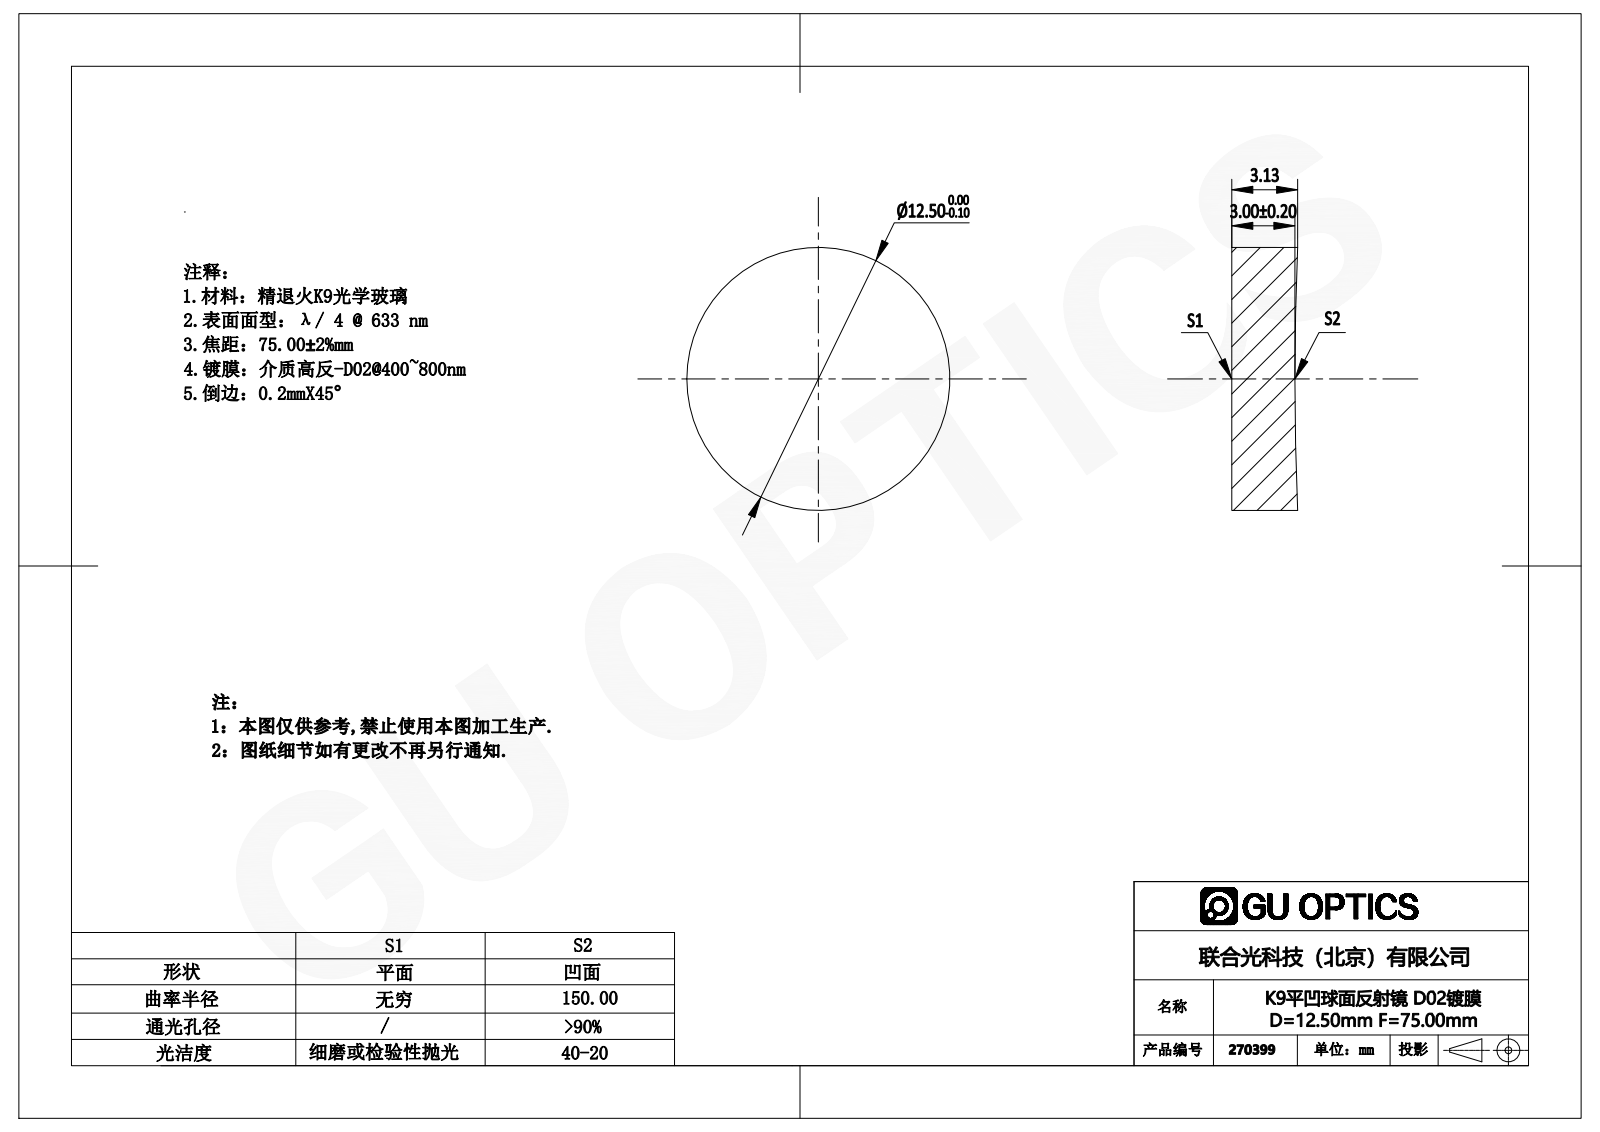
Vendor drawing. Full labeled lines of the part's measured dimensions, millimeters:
Part name (STEP PRODUCT): 270009
STEP written by: SolidWorks 2016 (AUTOMOTIVE_DESIGN)
Units: millimetres
Bodies: 1 solid, 5 faces (1 planar, 2 cylindrical, 2 other)
Overall size (bounding box): 12.5 × 12.5 × 3.13
Volume: 376 mm³ · Surface area: 368 mm²
Round bosses / shafts (diameter × count): ⌀12.5 ×1
